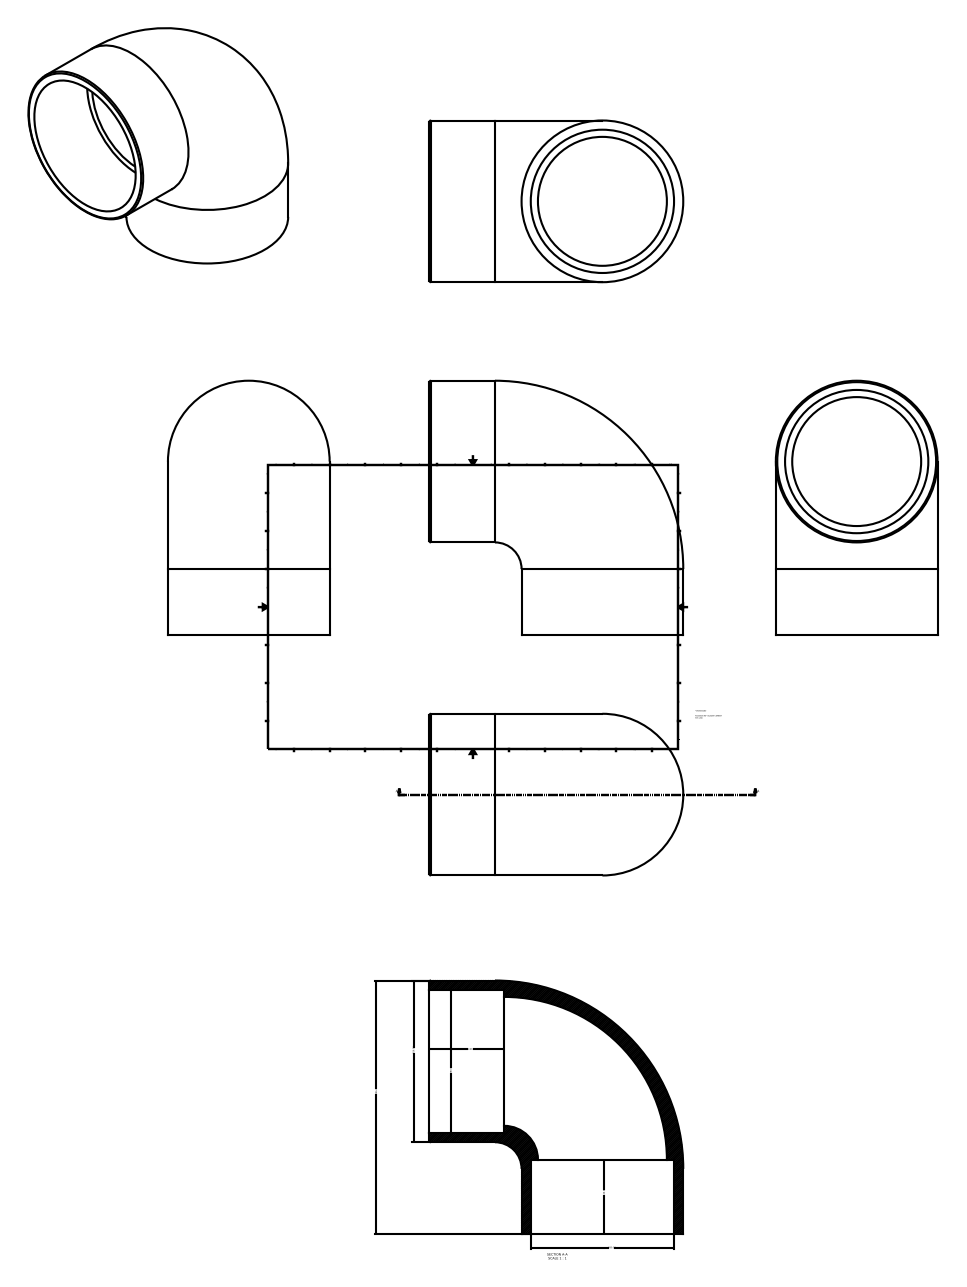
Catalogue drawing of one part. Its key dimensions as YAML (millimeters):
part_name: "(_AS)050500280"
step_written_by: "Autodesk Inventor 2015 (AUTOMOTIVE_DESIGN)"
units: millimeters
bodies: {solids: 1, faces: 11, planar: 4, cylindrical: 4, other: 3}
overall_size: [496, 496, 316]
volume: 12920000
surface_area: 1133000
round_holes:
  - {diameter: 280, count: 2}
round_bosses_or_shafts:
  - {diameter: 316, count: 2}
face_to_face_distances: [146]
